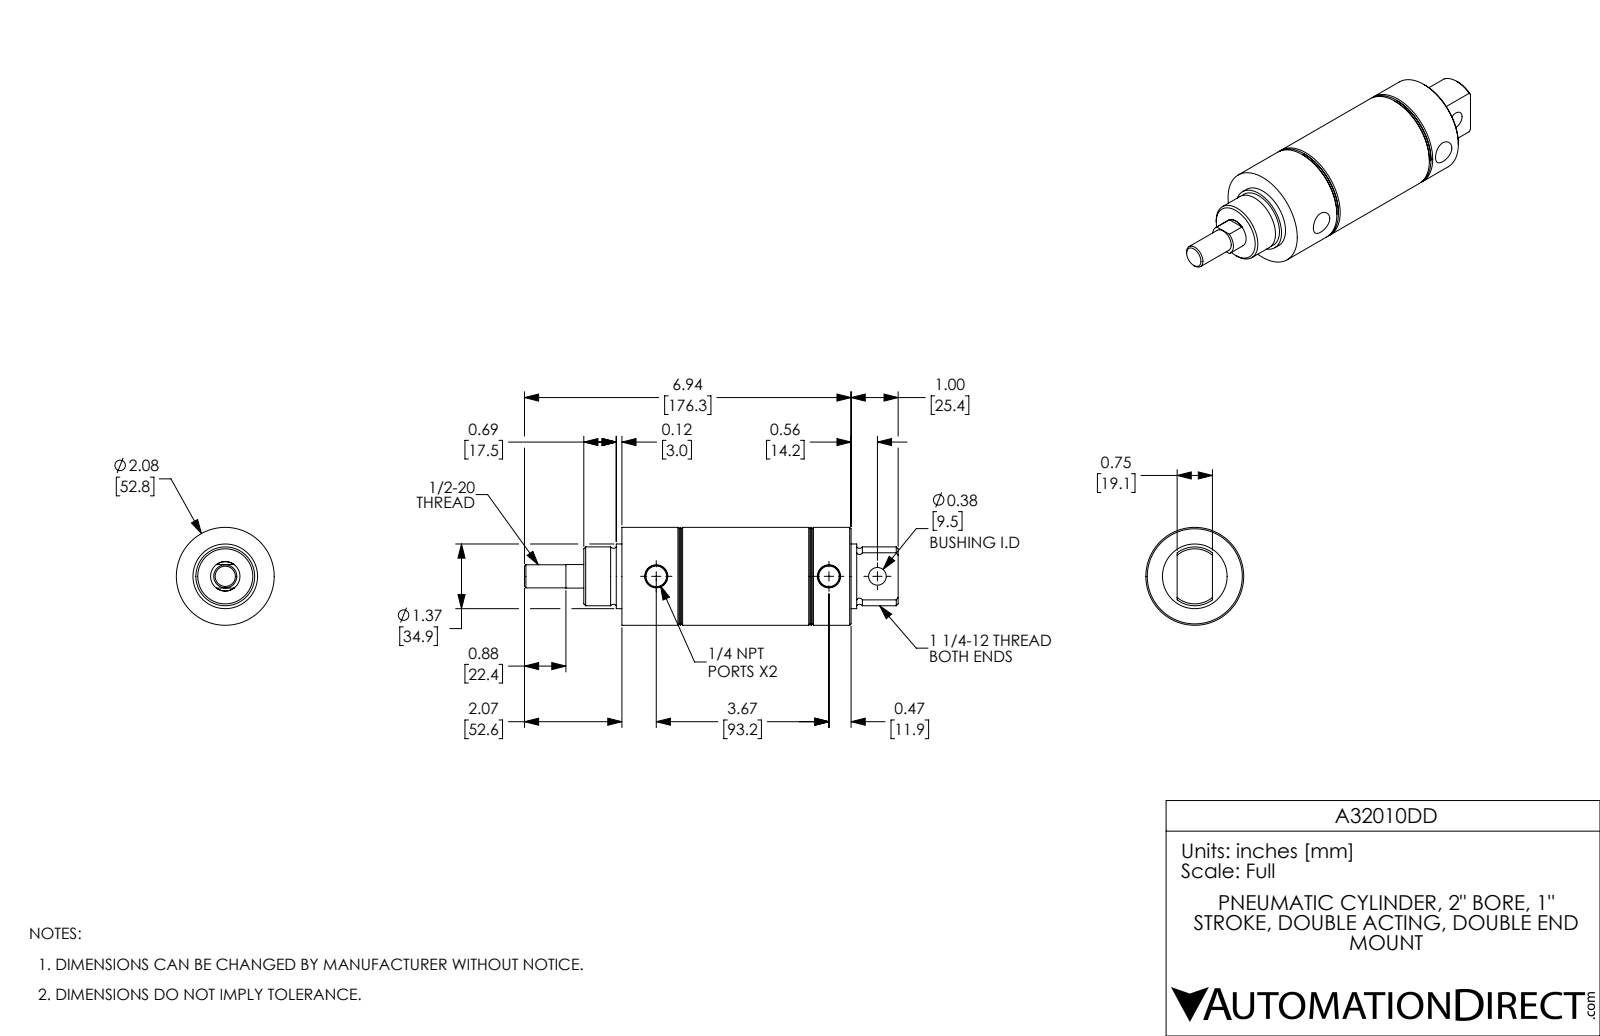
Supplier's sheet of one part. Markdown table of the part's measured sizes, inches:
| quantity | value |
| --- | --- |
| part name | A32010DD-MainBody; A32010DD-Rod; A32010DD |
| STEP written by | SolidWorks 2017 (AUTOMOTIVE_DESIGN) |
| units | inches |
| bodies | 2 solids, 88 faces (20 planar, 30 cylindrical, 38 other) |
| overall size | 7.94 × 2.08 × 2.08 |
| volume | 15.55 in³ |
| surface area | 87.05 in² |
| round holes (diameter × count) | 0.438 × 2, 0.375 × 1, 0.625 × 1, 2 × 1 |
| round bosses / shafts (diameter × count) | 2.08 × 1, 1.373 × 1, 1.25 × 1, 0.491 × 1 |
| main face-to-face distances | 1, 0.5, 1.5, 3.185, 3.185, 2.685, 1.685, 1.685, 2.185, 4.87 |
| hole center spacings | 1.03, 3.67, 4.7 |
